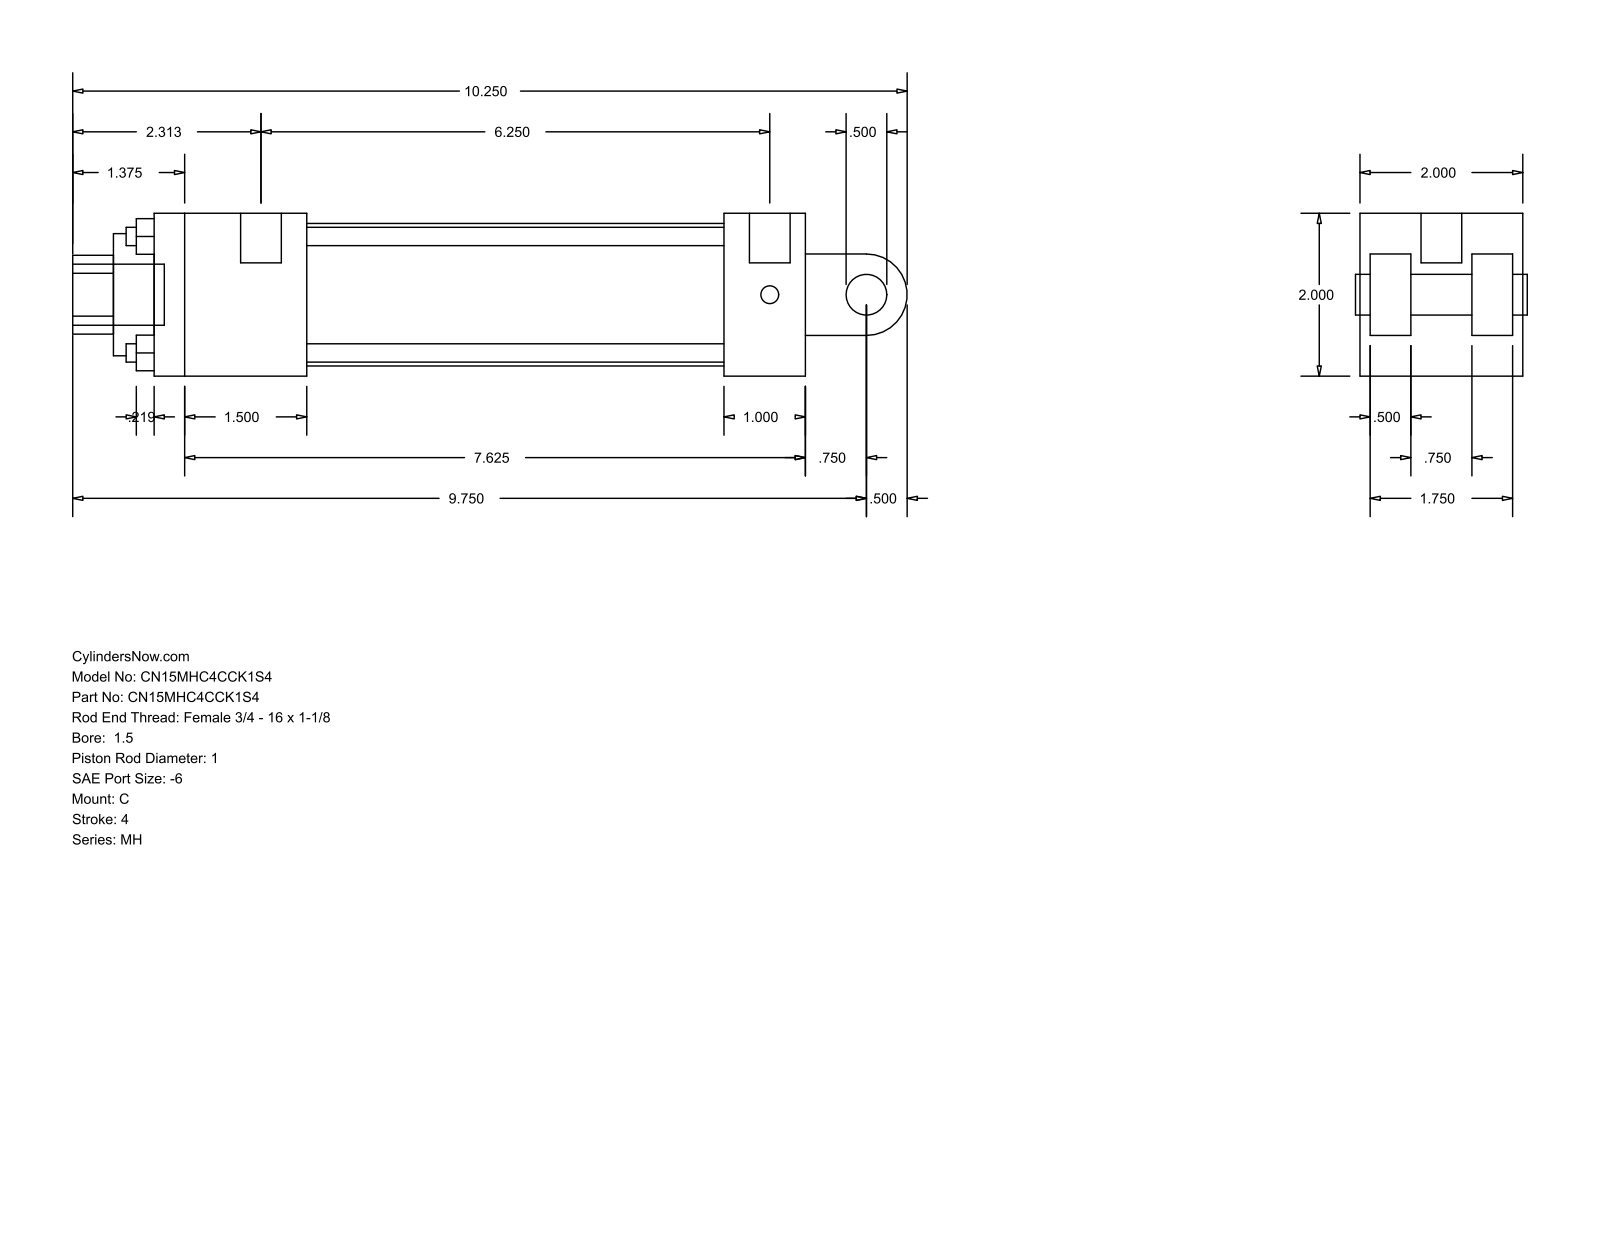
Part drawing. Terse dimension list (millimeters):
name: MH_C__0150_1
written by: GSSL Pune (CONFIG_CONTROL_DESIGN)
unit: mm
bodies: 0 solids, 99 faces (70 planar, 29 cylindrical, 0 other)
size: 260.35 × 50.8 × 50.8
holes: 4× ⌀5.71, 2× ⌀5.56, 1× ⌀12.7, 1× ⌀25.4, 1× ⌀38.1, 1× ⌀44.45
bosses: 2× ⌀12.7, 2× ⌀5.56, 1× ⌀19.05
rounds: 1× R12.29, 1× R12.7
face distances: 50.8, 12.7, 47.63, 3.17, 15.87, 25.4, 34.93, 31.76, 203.2, 38.1
hole spacings: 25.68, 36.32, 51.36
